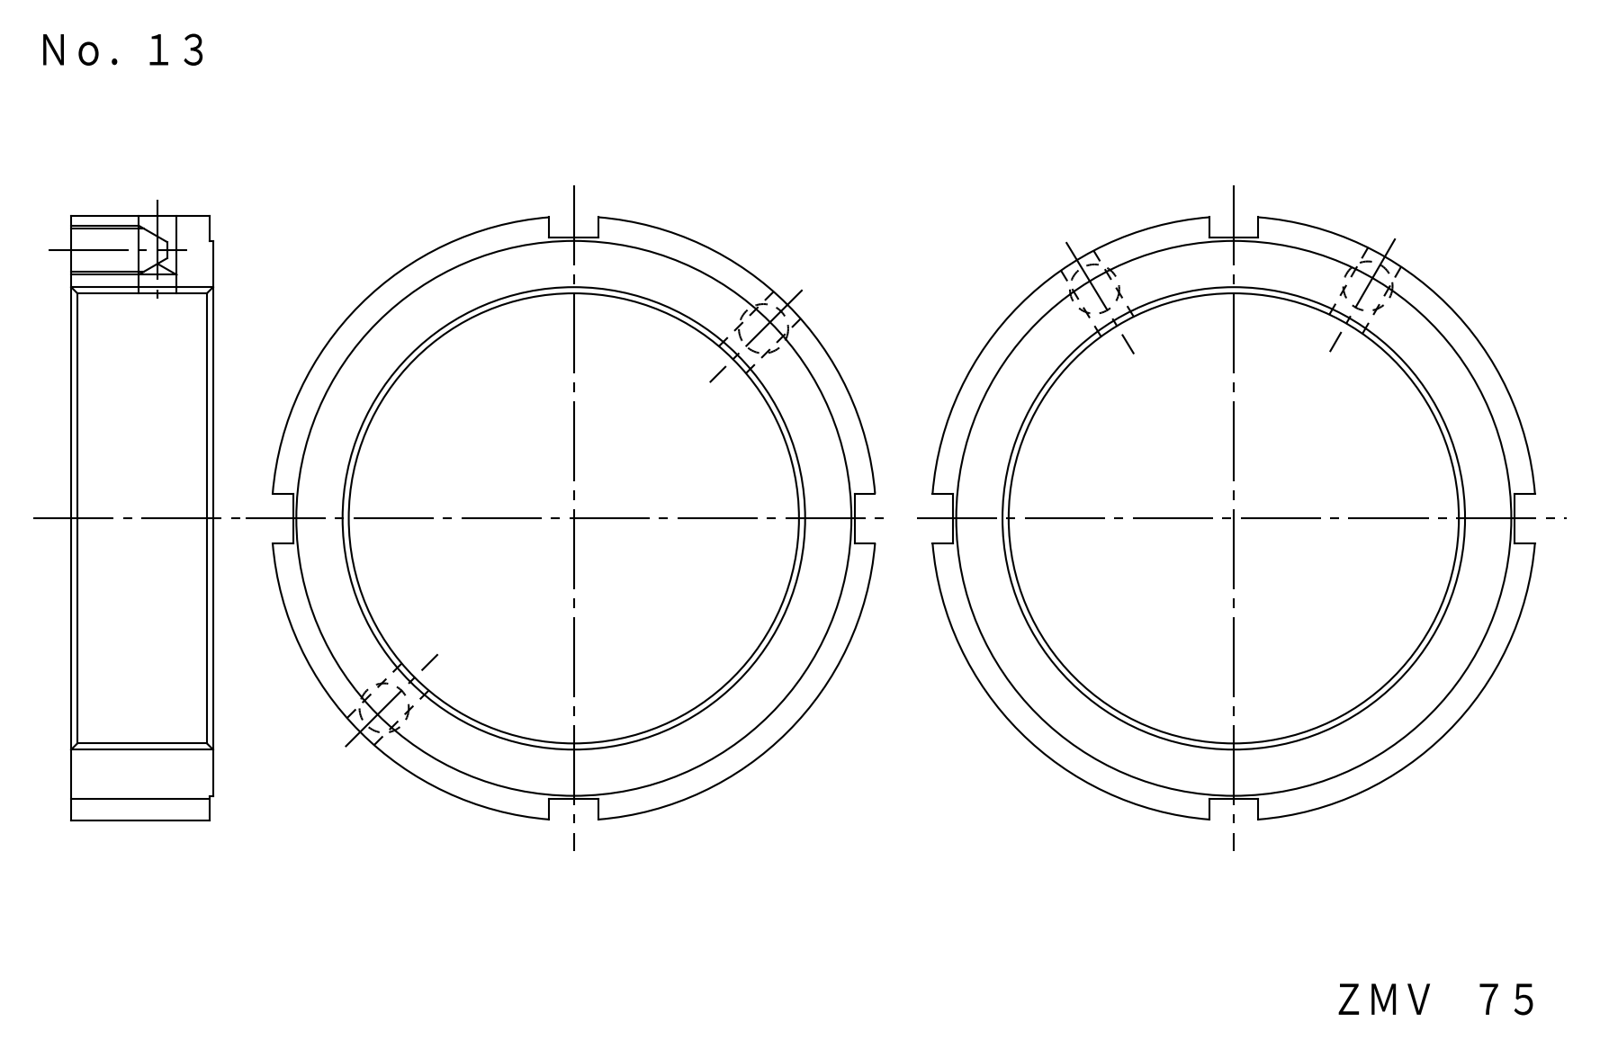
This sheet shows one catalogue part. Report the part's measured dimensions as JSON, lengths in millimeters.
{"part_name": "FKD ZMV75", "step_written_by": "Autodesk Inventor LT (CONFIG_CONTROL_DESIGN)", "units": "millimeters", "bodies": {"solids": 1, "faces": 29, "planar": 15, "cylindrical": 10, "other": 4}, "overall_size": [97.67, 97.67, 23], "volume_mm3": 67315, "surface_area_mm2": 19797, "round_holes": [[6.2, 2], [6.65, 2], [75, 1]], "round_bosses_or_shafts": [[98, 1], [90, 1]], "face_to_face_distances": [23, 0.5, 22.5, 41.5, 49.5, 91, 8], "hole_center_spacings": [43.5, 87]}
